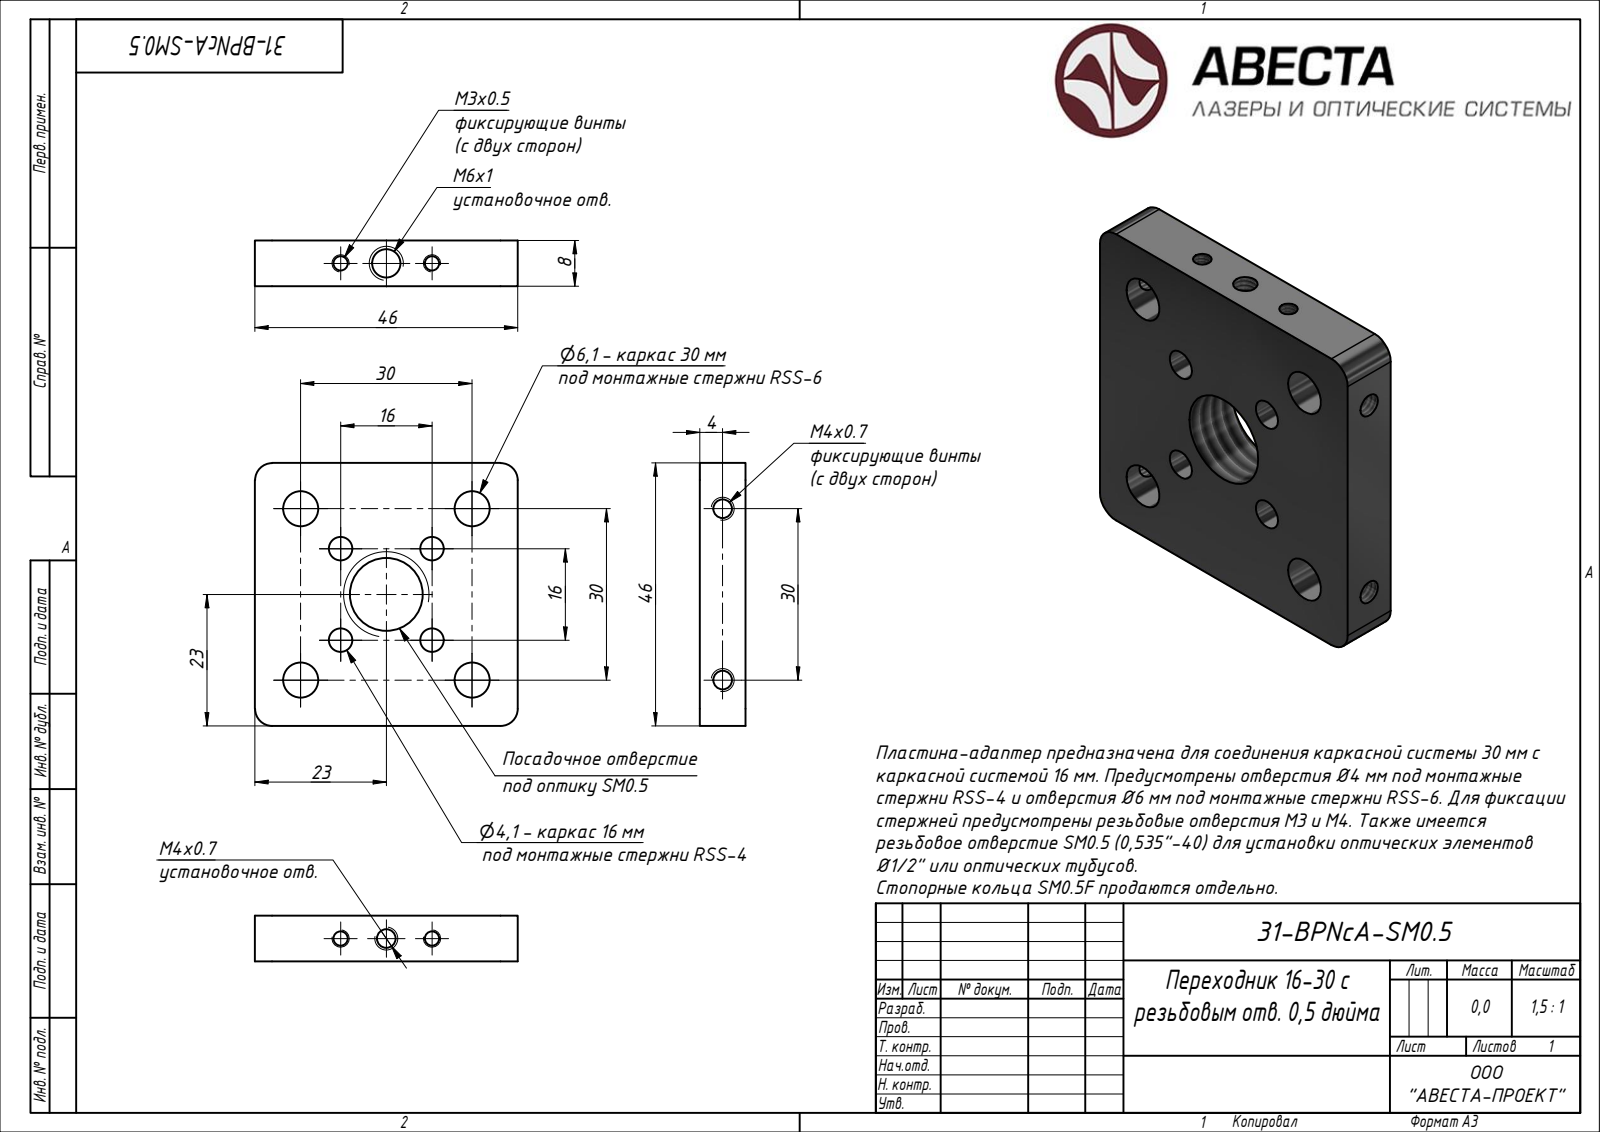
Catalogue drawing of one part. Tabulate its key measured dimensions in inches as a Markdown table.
| quantity | value |
| --- | --- |
| part name | 31-BPNcA-SM0.5 |
| STEP written by | Autodesk Inventor 2020 (AUTOMOTIVE_DESIGN) |
| units | inches |
| bodies | 1 solid, 31 faces (8 planar, 23 cylindrical, 0 other) |
| overall size | 1.811 × 1.811 × 0.315 |
| volume | 0.848 in³ |
| surface area | 10.95 in² |
| round holes (diameter × count) | 0.161 × 4, 0.24 × 4, 0.128 × 3, 0.097 × 2, 0.194 × 1, 0.503 × 1 |
| partial cylindrical surfaces (radius × count) | 0.118 × 4 |
| main face-to-face distances | 0.315, 1.811, 0.236, 1.575, 1.339 |
| hole center spacings | 0.946, 0.63, 1.181, 0.39, 0.445, 0.835, 1.281, 0.315 |
